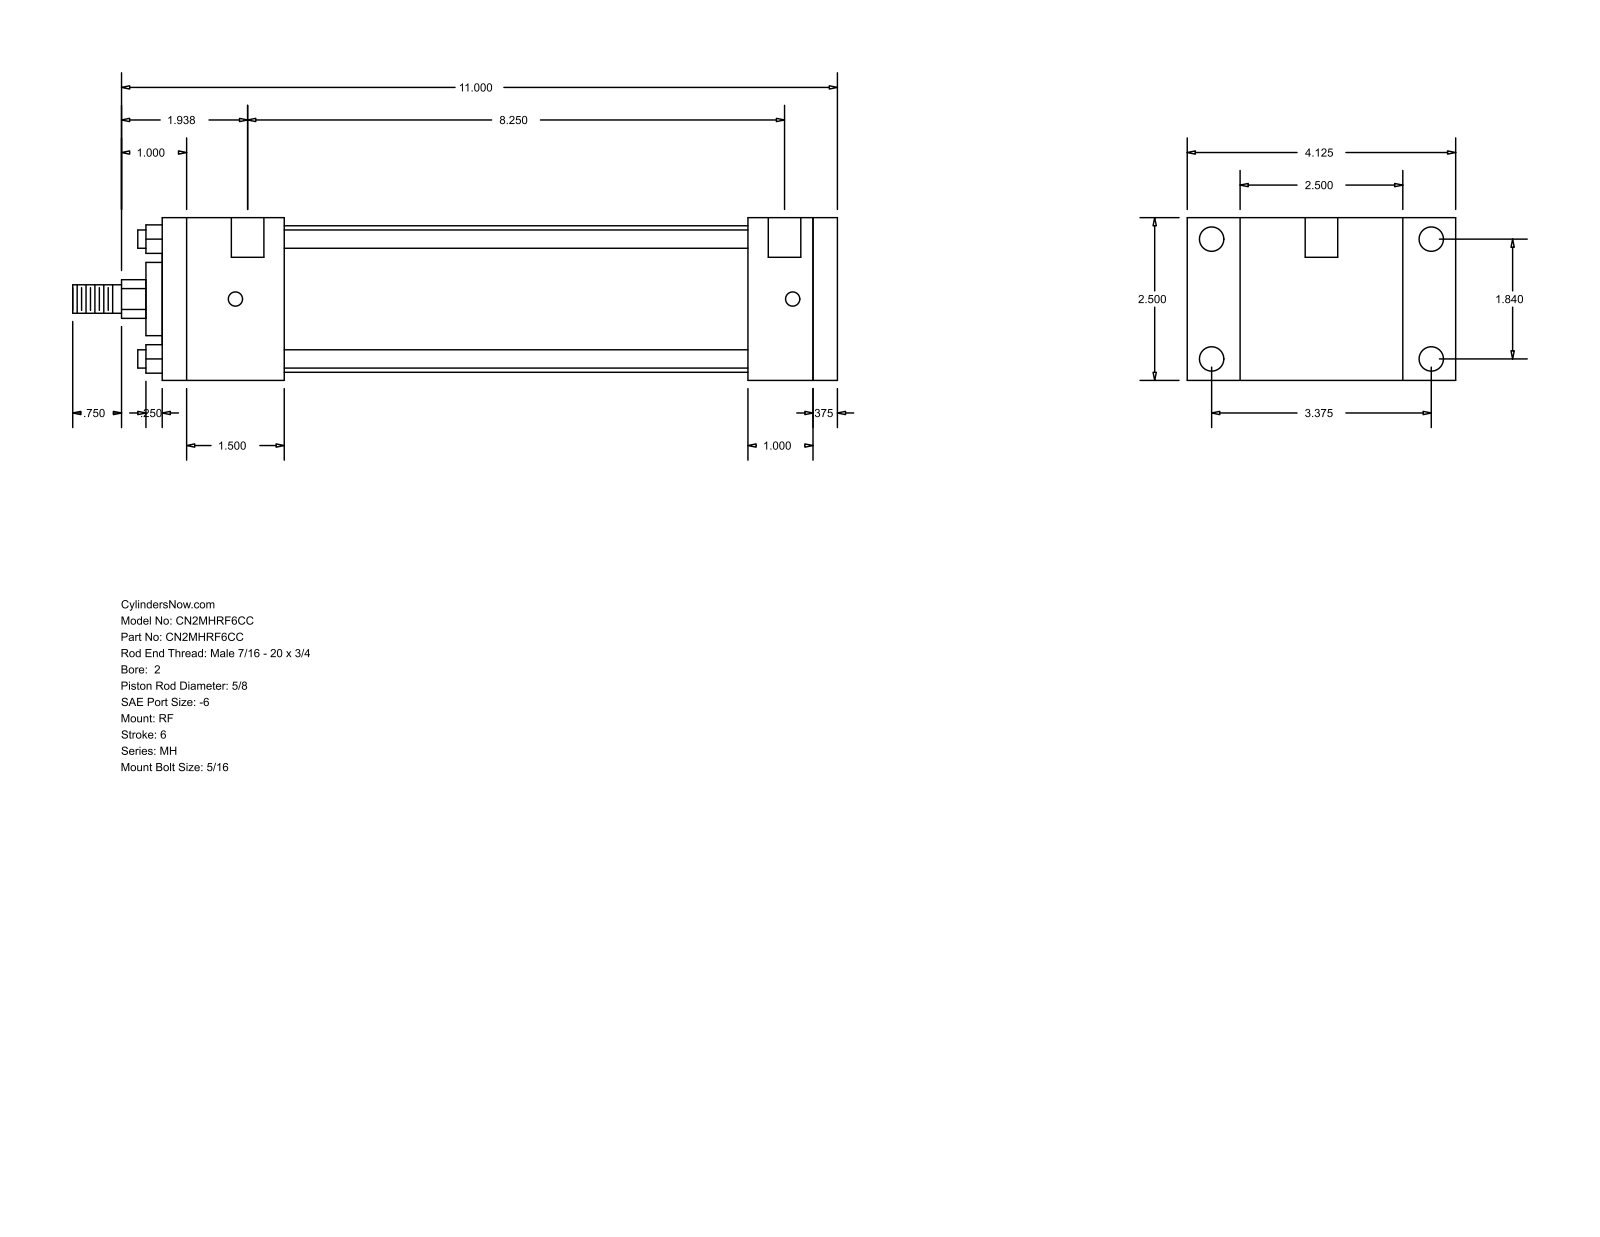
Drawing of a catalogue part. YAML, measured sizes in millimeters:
part_name: "MH_RF__0200_0.625"
step_written_by: "GSSL Pune (CONFIG_CONTROL_DESIGN)"
units: millimeters
bodies: {solids: 0, faces: 92, planar: 64, cylindrical: 28, other: 0}
overall_size: [298.45, 104.78, 63.5]
round_holes:
  - {diameter: 5.56, count: 4}
  - {diameter: 9.53, count: 4}
  - {diameter: 12.7, count: 2}
round_bosses_or_shafts:
  - {diameter: 7.14, count: 4}
  - {diameter: 57.15, count: 1}
  - {diameter: 28.57, count: 1}
  - {diameter: 15.88, count: 1}
  - {diameter: 11.11, count: 1}
partial_cylinders:
  - {radius: 7.54, count: 1}
face_to_face_distances: [63.5, 263.52, 254, 9.52, 34.93, 47.62, 228.59, 180.97, 206.38, 215.9]
hole_center_spacings: [46.74, 85.72, 97.63, 217.49, 3.18, 4.76, 209.55, 212.73]
